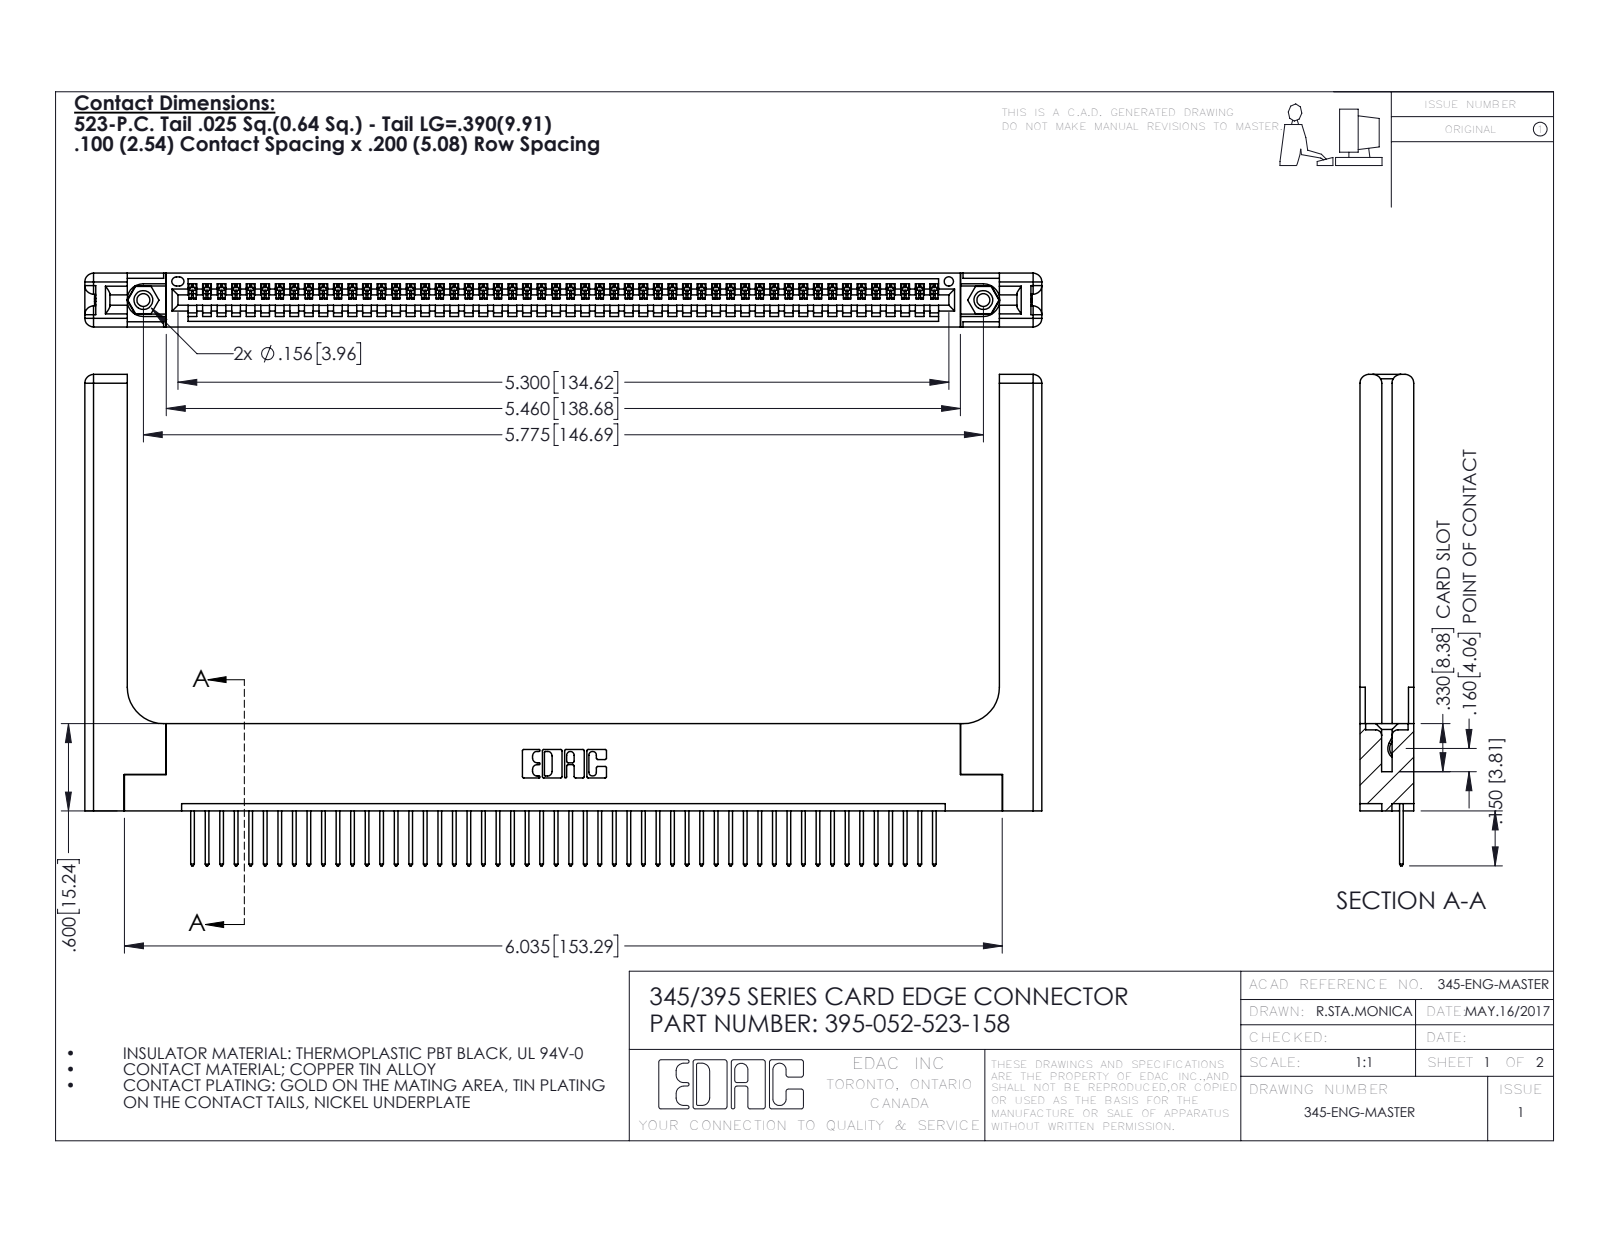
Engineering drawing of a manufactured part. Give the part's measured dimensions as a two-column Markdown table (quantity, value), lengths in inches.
| quantity | value |
| --- | --- |
| part name | 345-220-058_345-220-058; 345-250-001_345-250-001-102; 345-292-001_345-293-123; 345 Part_Flush Mounting Lugs - 0.156 Dia-TH (+1 more) |
| STEP written by | SolidWorks 2016 (CONFIG_CONTROL_DESIGN) |
| units | inches |
| bodies | 57 solids, 3398 faces (2308 planar, 1030 cylindrical, 60 other) |
| overall size | 6.579 × 3.377 × 0.37 |
| volume | 1.491 in³ |
| surface area | 41.34 in² |
| round holes (diameter × count) | 0.089 × 2, 0.125 × 2, 0.156 × 2, 0.064 × 1 |
| round bosses / shafts (diameter × count) | 0.155 × 2 |
| partial cylindrical surfaces (radius × count) | 0.006 × 104, 0.01 × 104, 0.01 × 22, 0.06 × 16, 0.007 × 6, 0.031 × 6, 0.026 × 3, 0.03 × 2 |
| main face-to-face distances | 0.072, 0.37, 0.298, 0.2, 0.098, 0.272, 0.025, 0.225, 0.148, 0.15 |
| hole center spacings | 0.27, 5.539, 5.775 |
